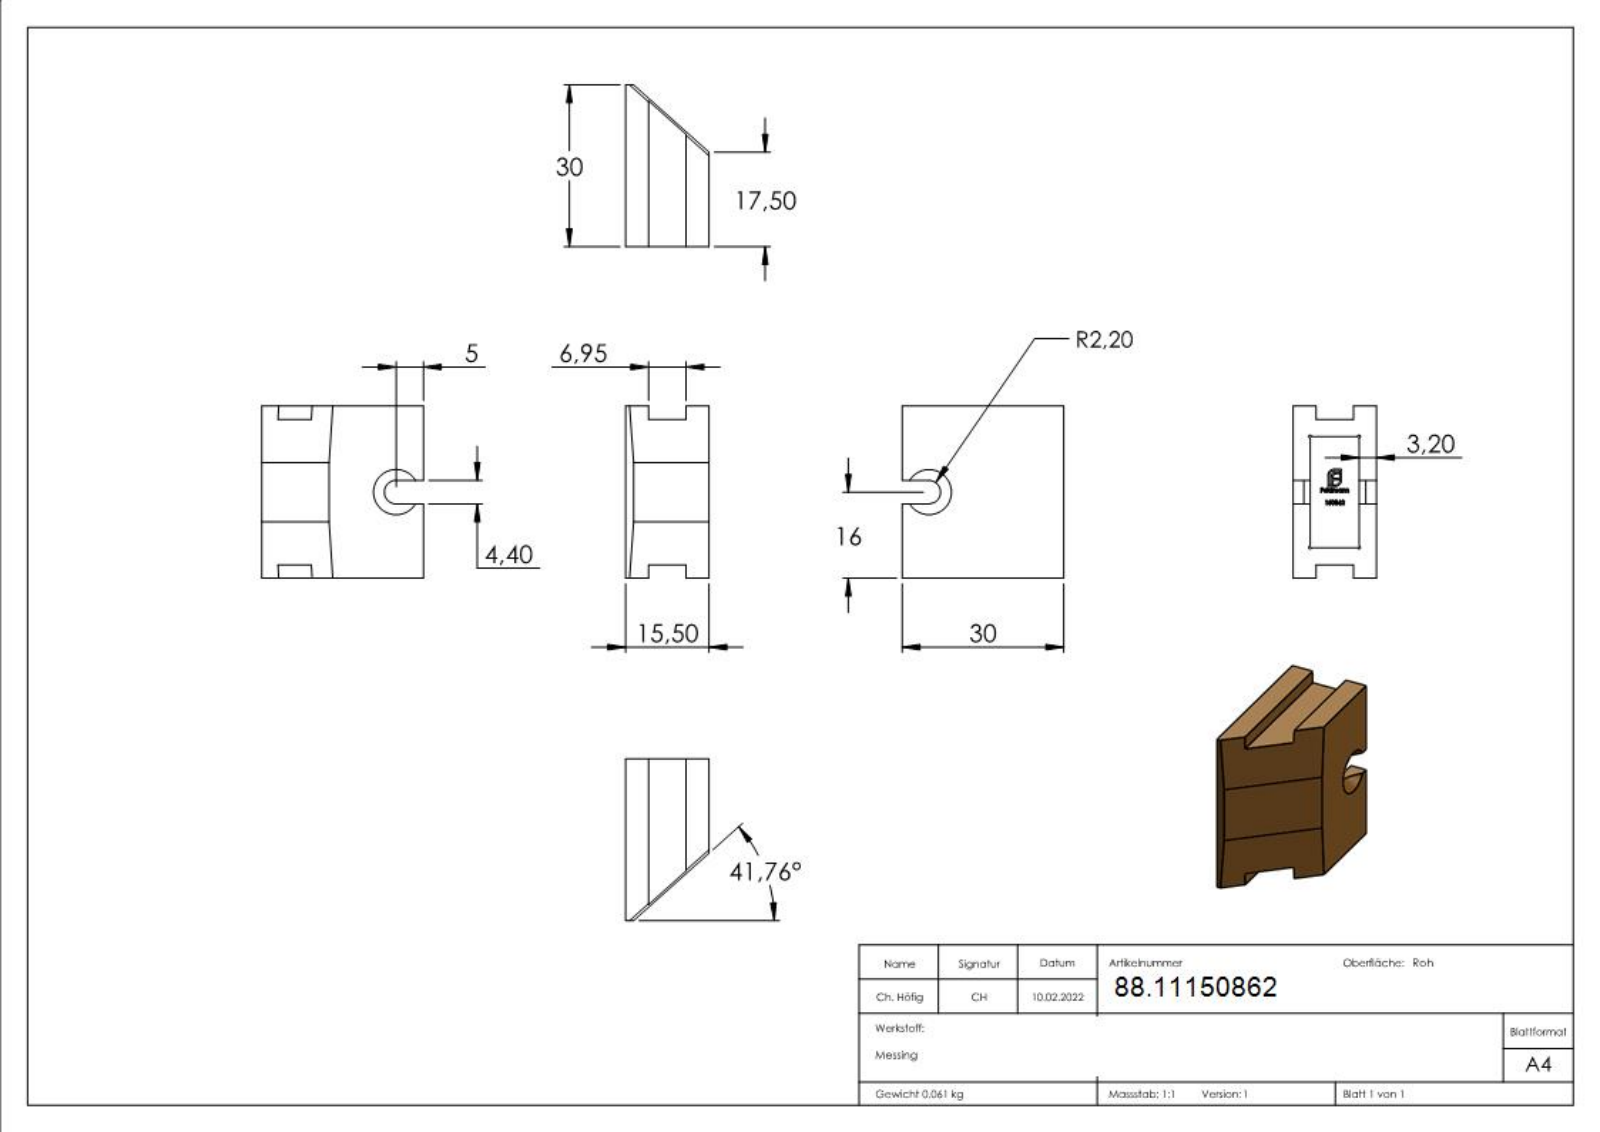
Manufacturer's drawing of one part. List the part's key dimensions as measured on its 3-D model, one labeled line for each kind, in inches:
Part name (STEP PRODUCT): 150862
STEP written by: SolidWorks 2018 (CONFIG_CONTROL_DESIGN)
Units: inches
Bodies: 1 solid, 276 faces (146 planar, 10 cylindrical, 120 other)
Overall size (bounding box): 1.26 × 1.181 × 0.61
Volume: 0.435 in³ · Surface area: 7.473 in²
Partial cylindrical surfaces — rounded edges, fillets, slot ends (radius × count): R0.01 ×4, R0.087 ×1
Main face-to-face distances: 0.126, 0.484, 0.61, 0.224, 1.035, 0.098, 1.161, 0.937, 0.358, 1.26
